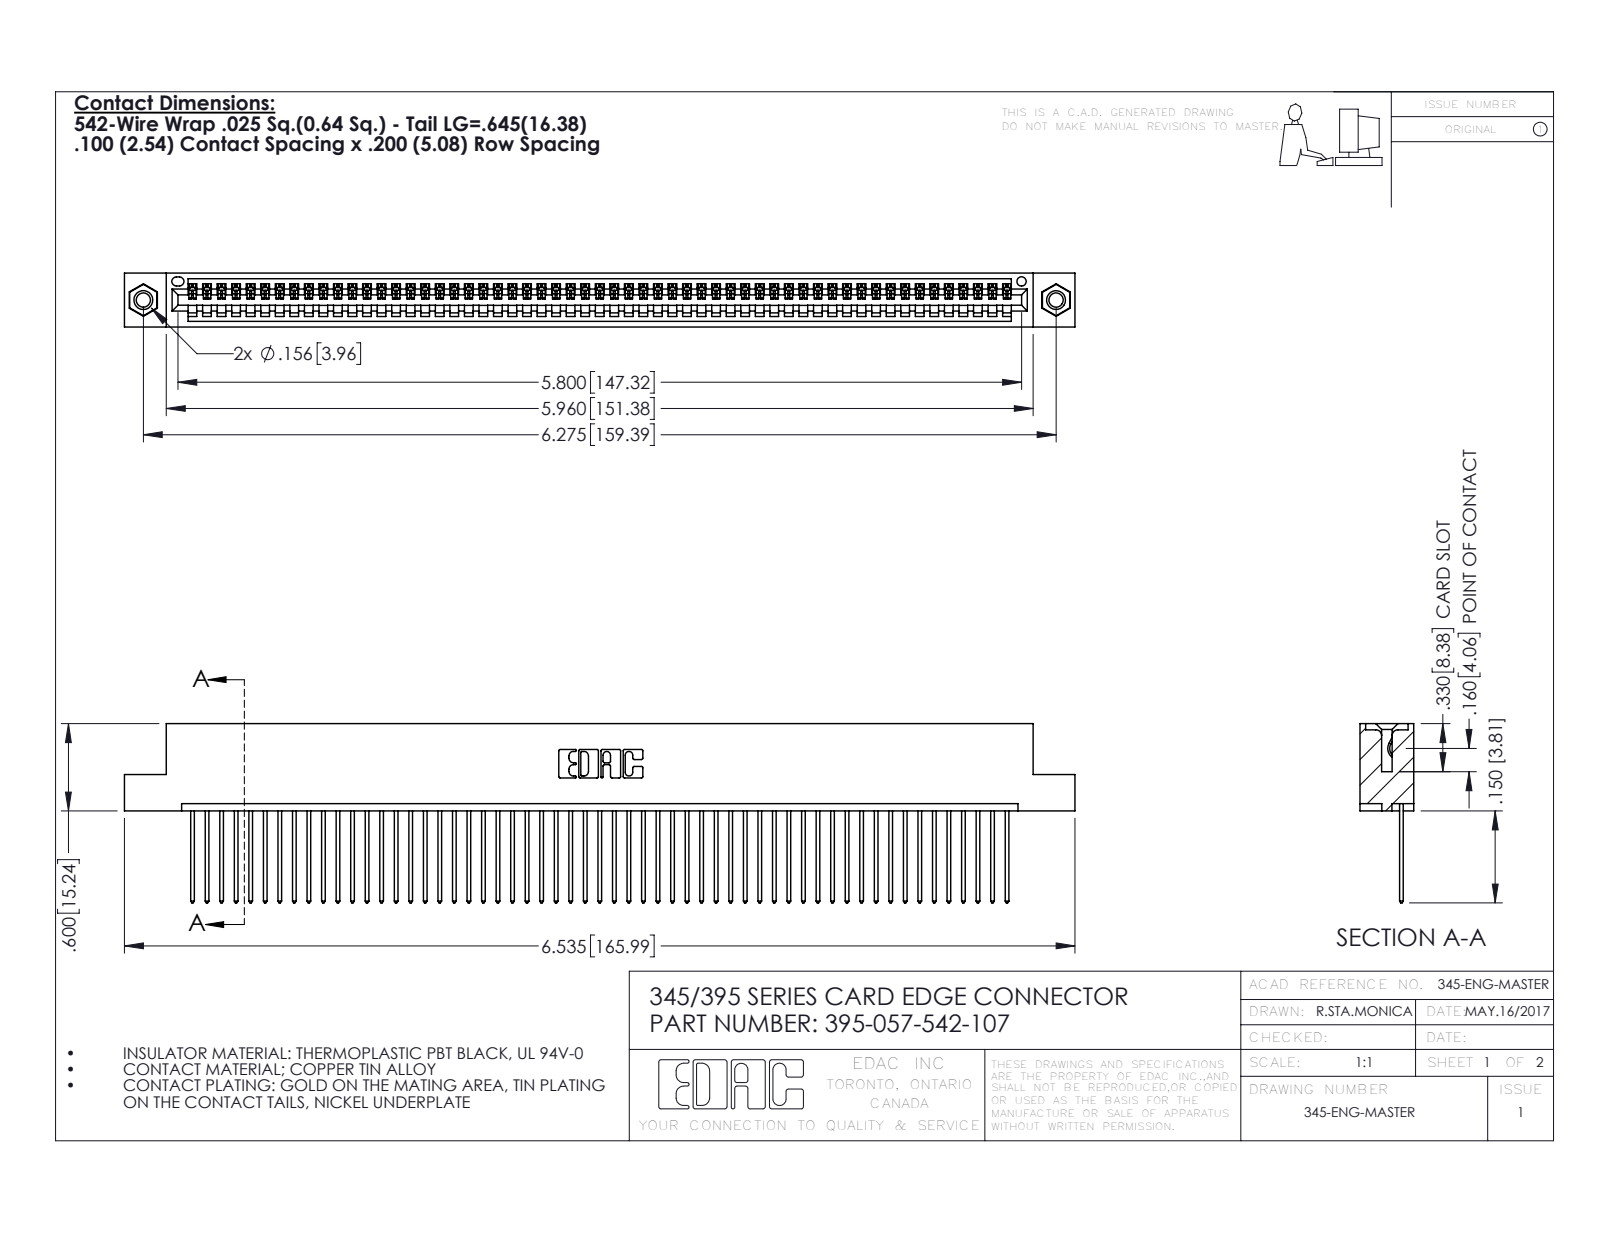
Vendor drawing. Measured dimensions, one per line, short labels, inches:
name: 345-250-001_345-250-005-103; 395-057-542-107; 345-292-001_345-293-142; 345 Part_Flush Mounting Lugs - 0.156 Dia-TI
written by: SolidWorks 2016 (CONFIG_CONTROL_DESIGN)
unit: in
bodies: 60 solids, 3492 faces (2392 planar, 1084 cylindrical, 16 other)
size: 6.535 × 1.232 × 0.37
volume: 0.977 in³; area: 34.57 in²
holes: 2× ⌀0.098, 2× ⌀0.125, 2× ⌀0.156, 1× ⌀0.064
bosses: 2× ⌀0.155
rounds: 114× R0.006, 114× R0.01, 22× R0.01, 6× R0.007, 6× R0.031, 3× R0.026, 2× R0.031, 2× R0.04
face distances: 0.072, 0.298, 0.098, 0.272, 0.025, 0.37, 0.2, 0.225, 0.149, 0.072
hole spacings: 0.27, 6.039, 6.275
